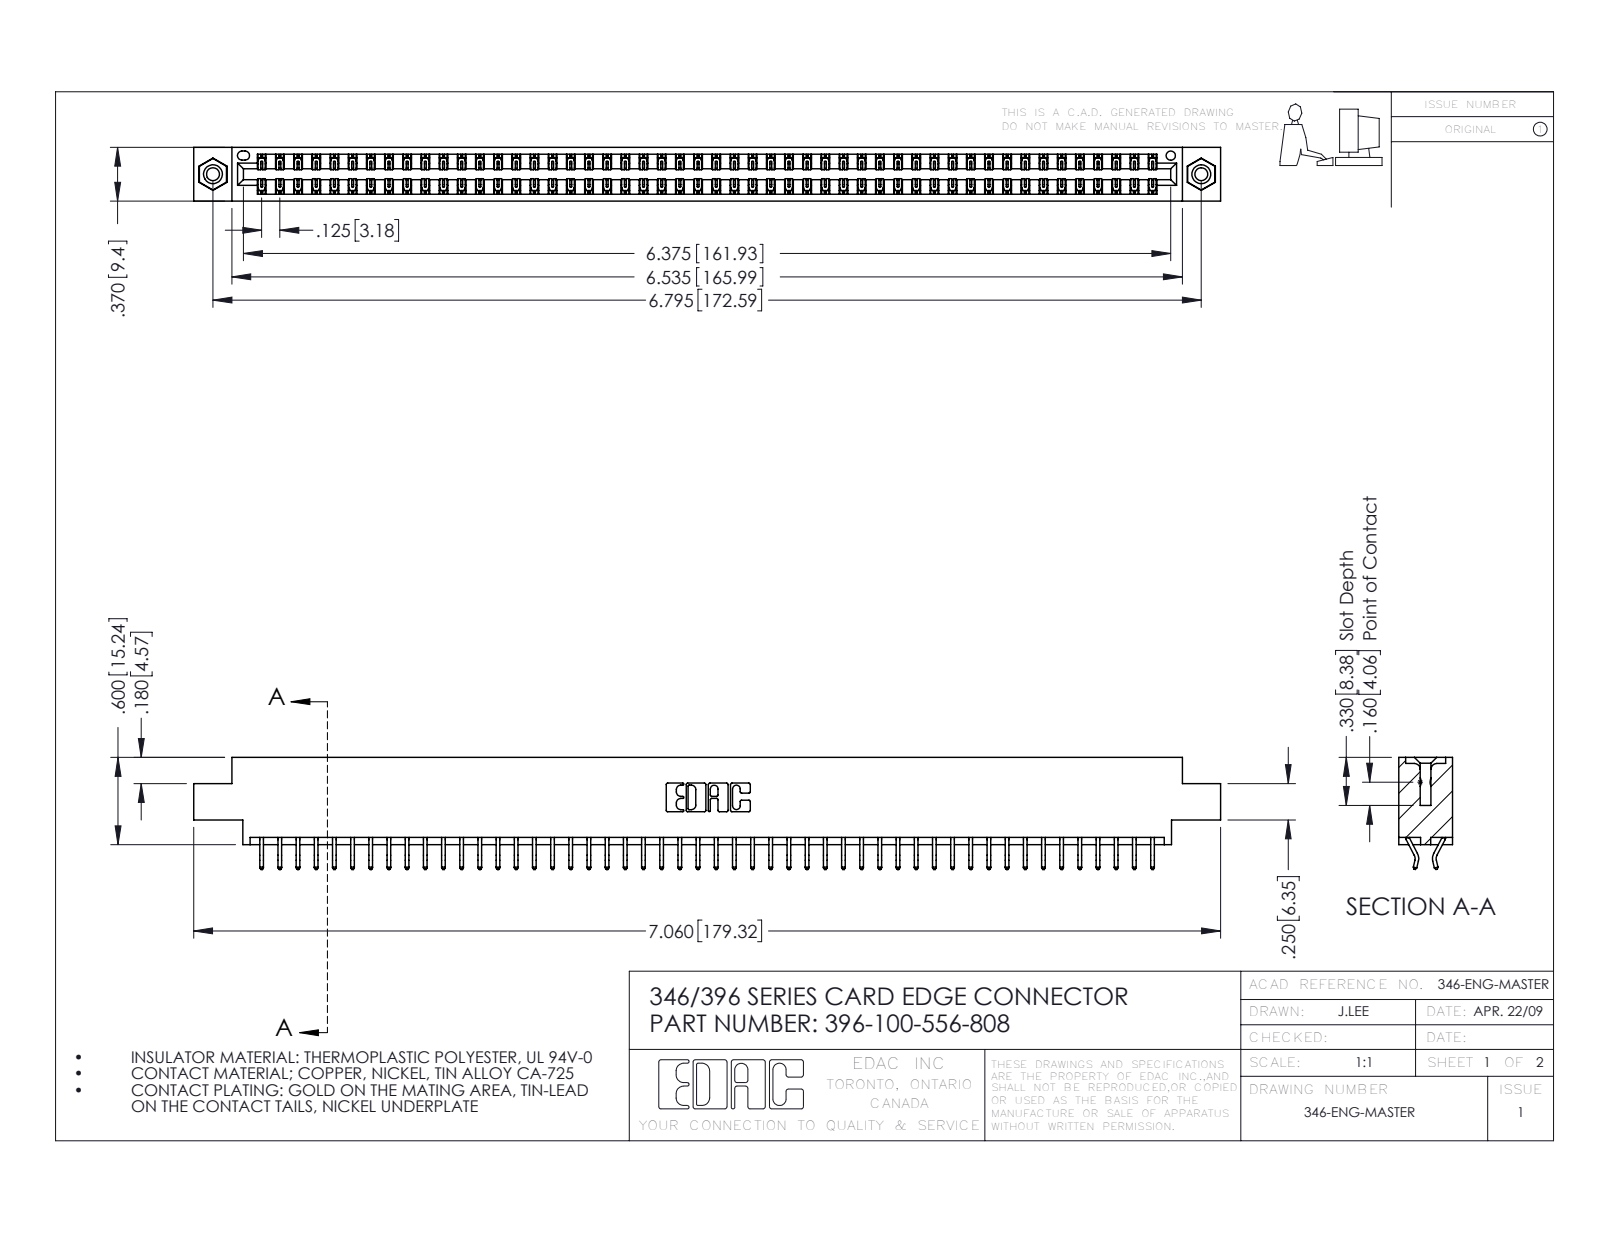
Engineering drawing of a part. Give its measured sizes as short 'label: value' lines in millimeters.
name: 345-292-001_556 Tail; 396-100-556-808; 345-250-001_345-250-003-102; 346 Part_0.170 Offset - 0.156 Dia-TI
written by: SolidWorks 2016 (CONFIG_CONTROL_DESIGN)
unit: mm
bodies: 103 solids, 5986 faces (4012 planar, 1958 cylindrical, 16 other)
size: 179.3 × 19.6 × 9.4
volume: 17 390 mm³; area: 24 130 mm²
holes: 2× ⌀2.3, 2× ⌀3.2, 2× ⌀4, 1× ⌀1.6
bosses: 2× ⌀3.9
rounds: 150× R0.2, 22× R0.3, 6× R0.2, 6× R0.8, 3× R0.7, 2× R0.3, 2× R0.4, 2× R0.6
face distances: 1.2, 8.2, 9.4, 6.4, 0.6, 1.8, 7.6, 7, 5.6, 3.8
hole spacings: 6.2, 167.3, 172.6
